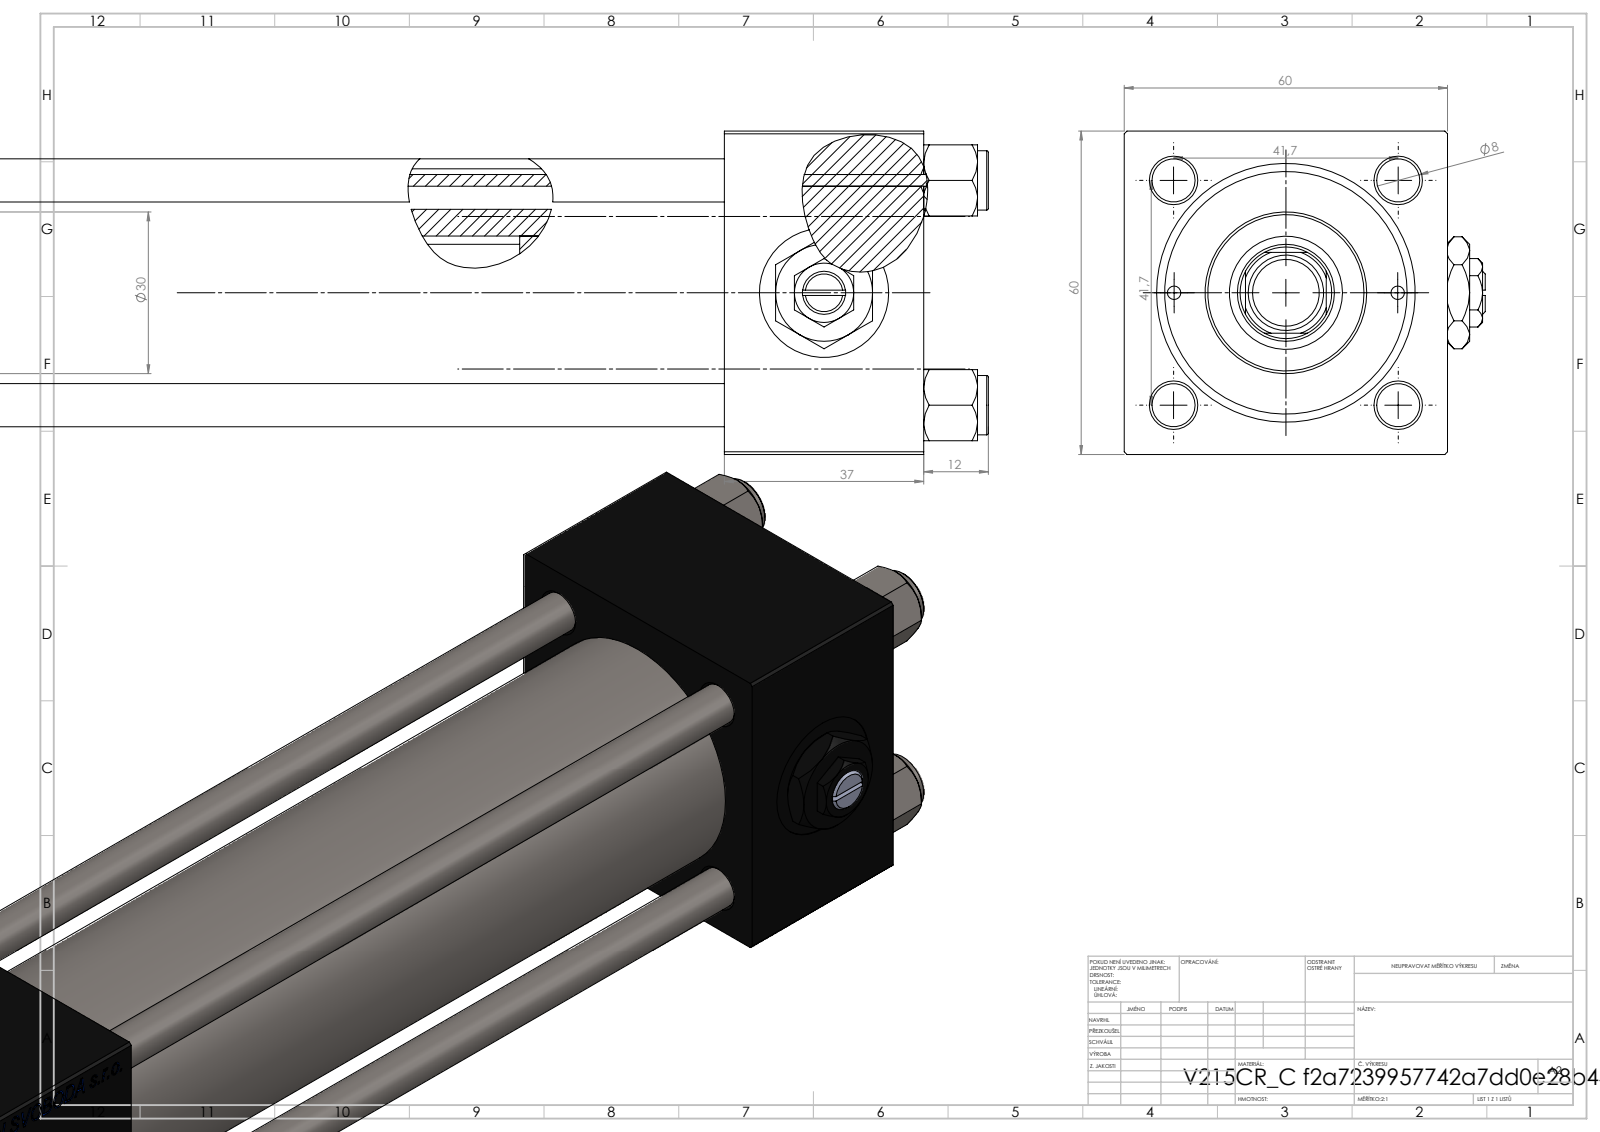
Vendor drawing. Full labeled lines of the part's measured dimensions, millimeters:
Part name (STEP PRODUCT): V215_VC_A; NUT_M5_C; ROD_END_AH; Zatka_pro_OIL_PORT (+3 more)
STEP written by: SolidWorks 2019 (CONFIG_CONTROL_DESIGN)
Units: millimetres
Bodies: 14 solids, 1270 faces (580 planar, 106 cylindrical, 584 other)
Overall size (bounding box): 308 × 67 × 60
Volume: 492 329 mm³ · Surface area: 154 315 mm²
Round holes (diameter × count): ⌀8 ×4, ⌀2.5 ×2, ⌀7 ×2, ⌀16.66 ×2, ⌀24 ×2, ⌀8.5 ×1, ⌀18 ×1, ⌀21 ×1, ⌀31 ×1, ⌀40 ×1, ⌀45 ×1
Round bosses / shafts (diameter × count): ⌀11 ×4, ⌀46 ×1, ⌀30 ×1, ⌀14 ×1, ⌀12 ×1
Partial cylindrical surfaces — rounded edges, fillets, slot ends (radius × count): R8.5 ×1
Main face-to-face distances: 60, 37, 253, 216, 53, 200, 163, 224.3, 187.3, 24.3
Hole centre spacings: 20.85, 29.49, 41.7, 46.53, 20.75, 58.97, 41.5, 197.5
